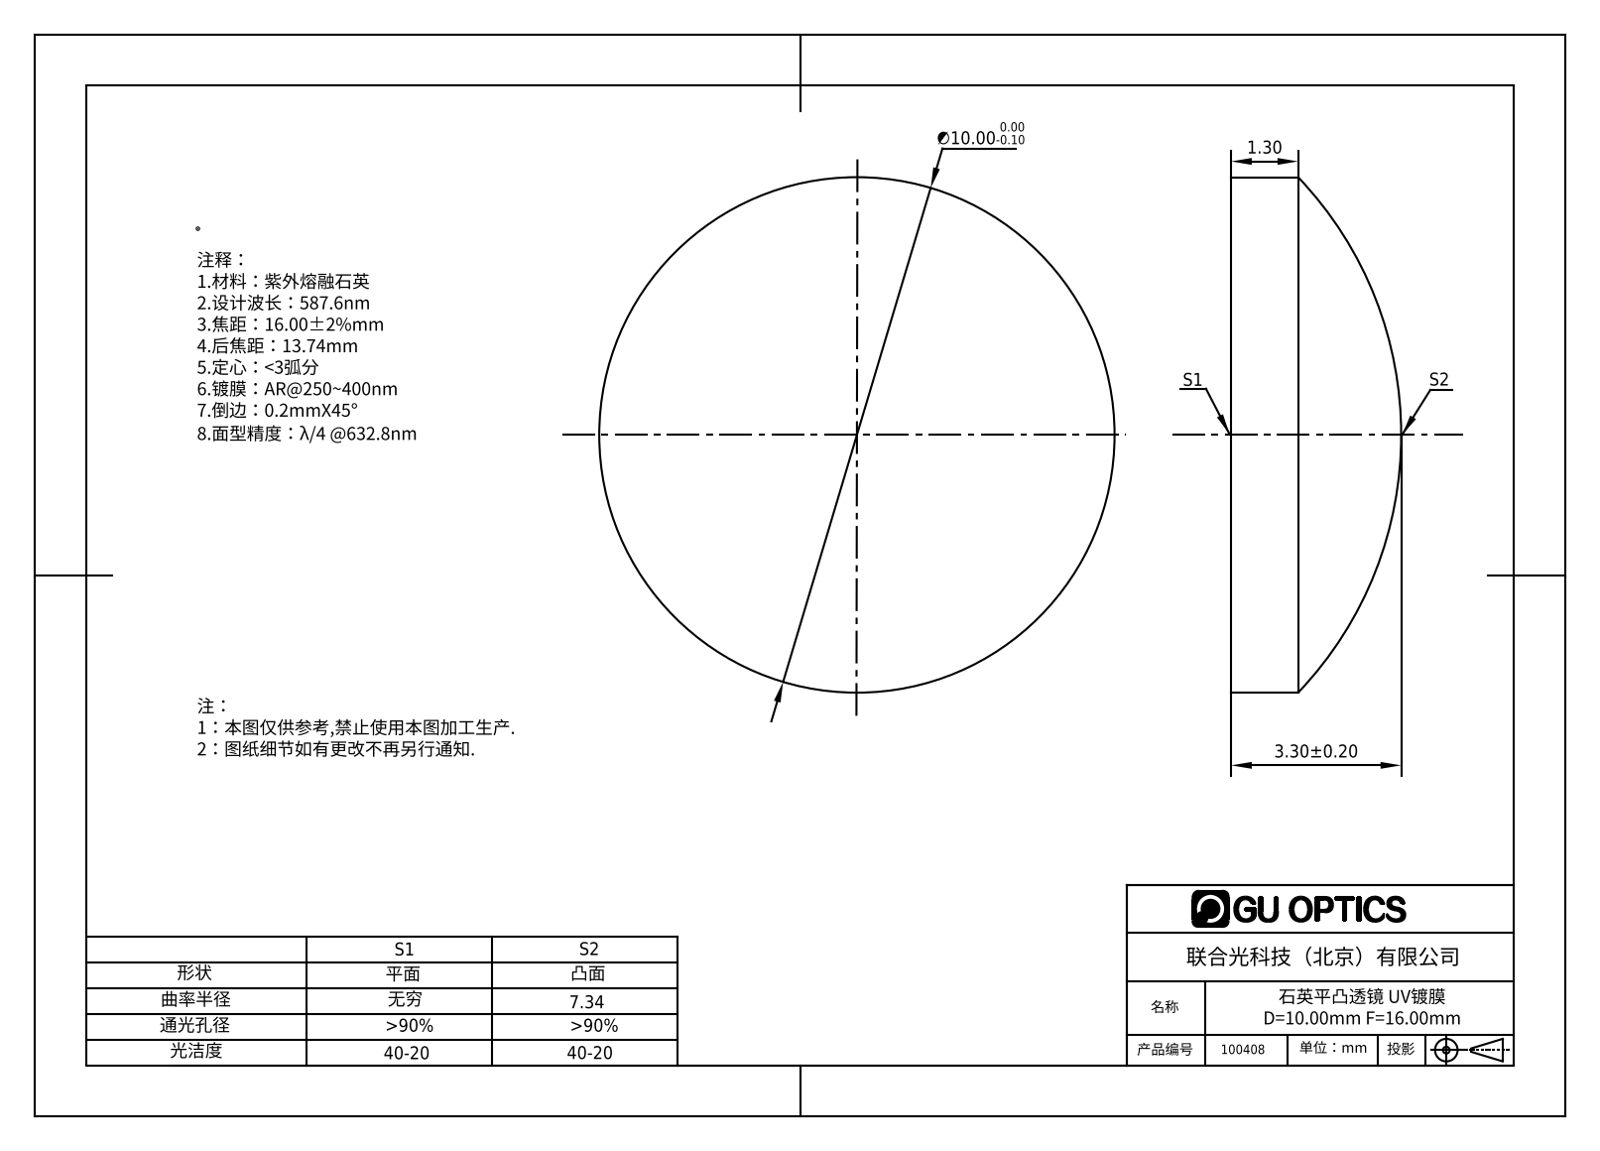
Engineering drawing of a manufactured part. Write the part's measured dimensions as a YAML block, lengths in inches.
part_name: "100358"
step_written_by: "SolidWorks 2016 (AUTOMOTIVE_DESIGN)"
units: inches
bodies: {solids: 1, faces: 5, planar: 1, cylindrical: 2, other: 2}
overall_size: [0.394, 0.394, 0.13]
volume: 0.011
surface_area: 0.326
round_bosses_or_shafts:
  - {diameter: 0.394, count: 1}
